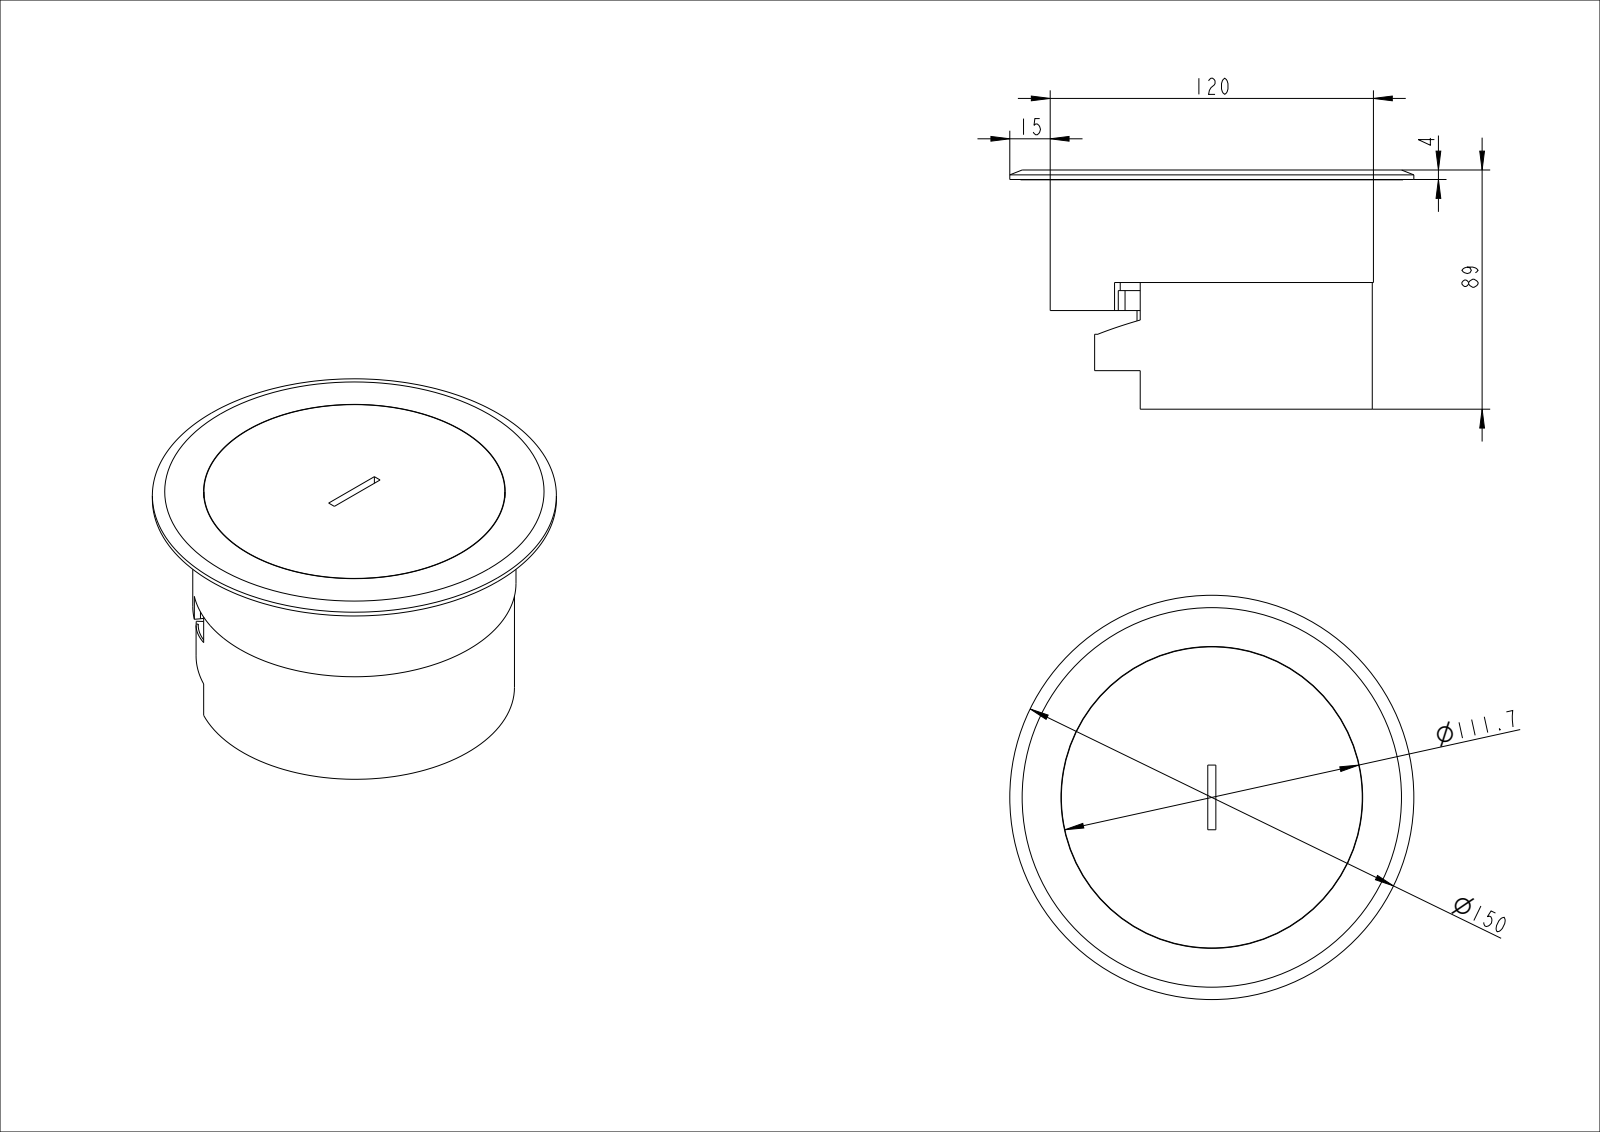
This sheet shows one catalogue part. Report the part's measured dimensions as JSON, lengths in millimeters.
{"part_name": "BSR_BECHERUNTERTEIL; BSR_BECHEROBERTEIL; BSR_GERTEAUFNAHME0; BSM012KUN (+3 more)", "step_written_by": "CREO PARAMETRIC BY PTC INC, 2022024 (AUTOMOTIVE_DESIGN)", "units": "millimeters", "bodies": {"solids": 6, "faces": 321, "planar": 260, "cylindrical": 59, "other": 2}, "overall_size": [150, 150, 88.75], "volume_mm3": 340688, "surface_area_mm2": 198642, "round_holes": [[5.7, 4], [2.73, 2], [38.3, 2], [2, 1], [3.6, 1], [85, 1], [112, 1], [115.4, 1], [145.02, 1]], "round_bosses_or_shafts": [[4.69, 2], [150, 1], [142, 1], [120, 1], [115.64, 1], [111.7, 1]], "partial_cylinders_radius": [[50, 2], [51, 1], [52, 1], [53, 1], [54.45, 1], [55, 1], [56.5, 1], [57.25, 1]], "face_to_face_distances": [1.5, 2.25, 36.6, 85, 38.1, 86.5, 88.75, 87.25, 48.4, 50.65], "hole_center_spacings": [8.85, 45, 17.68, 43.12, 15.83, 21.17, 22.93, 24.23]}
